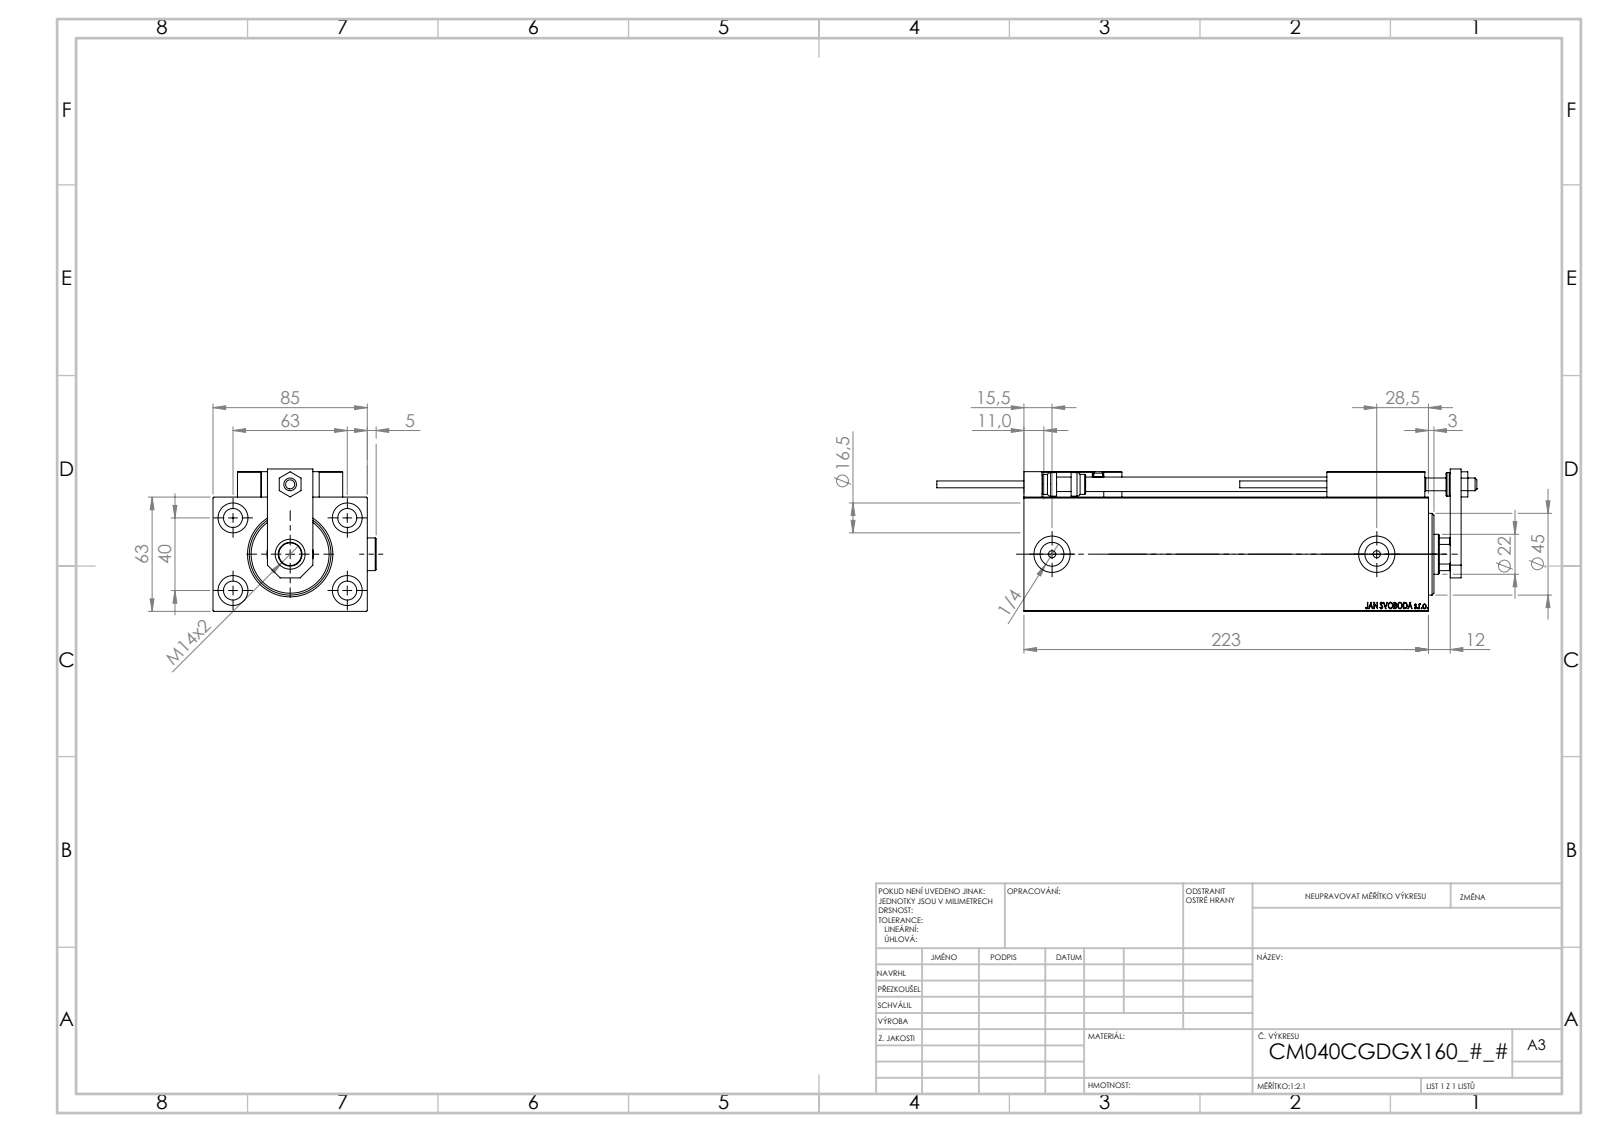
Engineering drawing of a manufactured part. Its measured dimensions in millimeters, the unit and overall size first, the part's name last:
Units: millimetres
Overall size (bounding box): 297.7 × 89.9 × 78.5
Round holes (diameter × count): ⌀4 ×6, ⌀8 ×5, ⌀16.5 ×5, ⌀3.2 ×4, ⌀10.5 ×4, ⌀5 ×2, ⌀13.16 ×2, ⌀20 ×2, ⌀7 ×1, ⌀12.5 ×1, ⌀22 ×1, ⌀25.5 ×1
Round bosses / shafts (diameter × count): ⌀18 ×2, ⌀5 ×2, ⌀3.8 ×2, ⌀13 ×1, ⌀11 ×1
Partial cylindrical surfaces — rounded edges, fillets, slot ends (radius × count): R0.3 ×30, R3 ×2, R10.5 ×1
Main face-to-face distances: 63, 85, 12, 211, 223, 14, 77, 15, 18, 30
Hole centre spacings: 37.31, 11.37, 20, 29.59, 29.69, 36.06, 36.53, 40
Volume: 1 020 000 mm³ · Surface area: 192 098 mm²
Bodies: 25 solids, 1336 faces (594 planar, 204 cylindrical, 538 other)
Part name (STEP PRODUCT): SWITCH X; TYC_L79; Block; NUT_D12 (+8 more)
STEP written by: SolidWorks 2019 (CONFIG_CONTROL_DESIGN)
